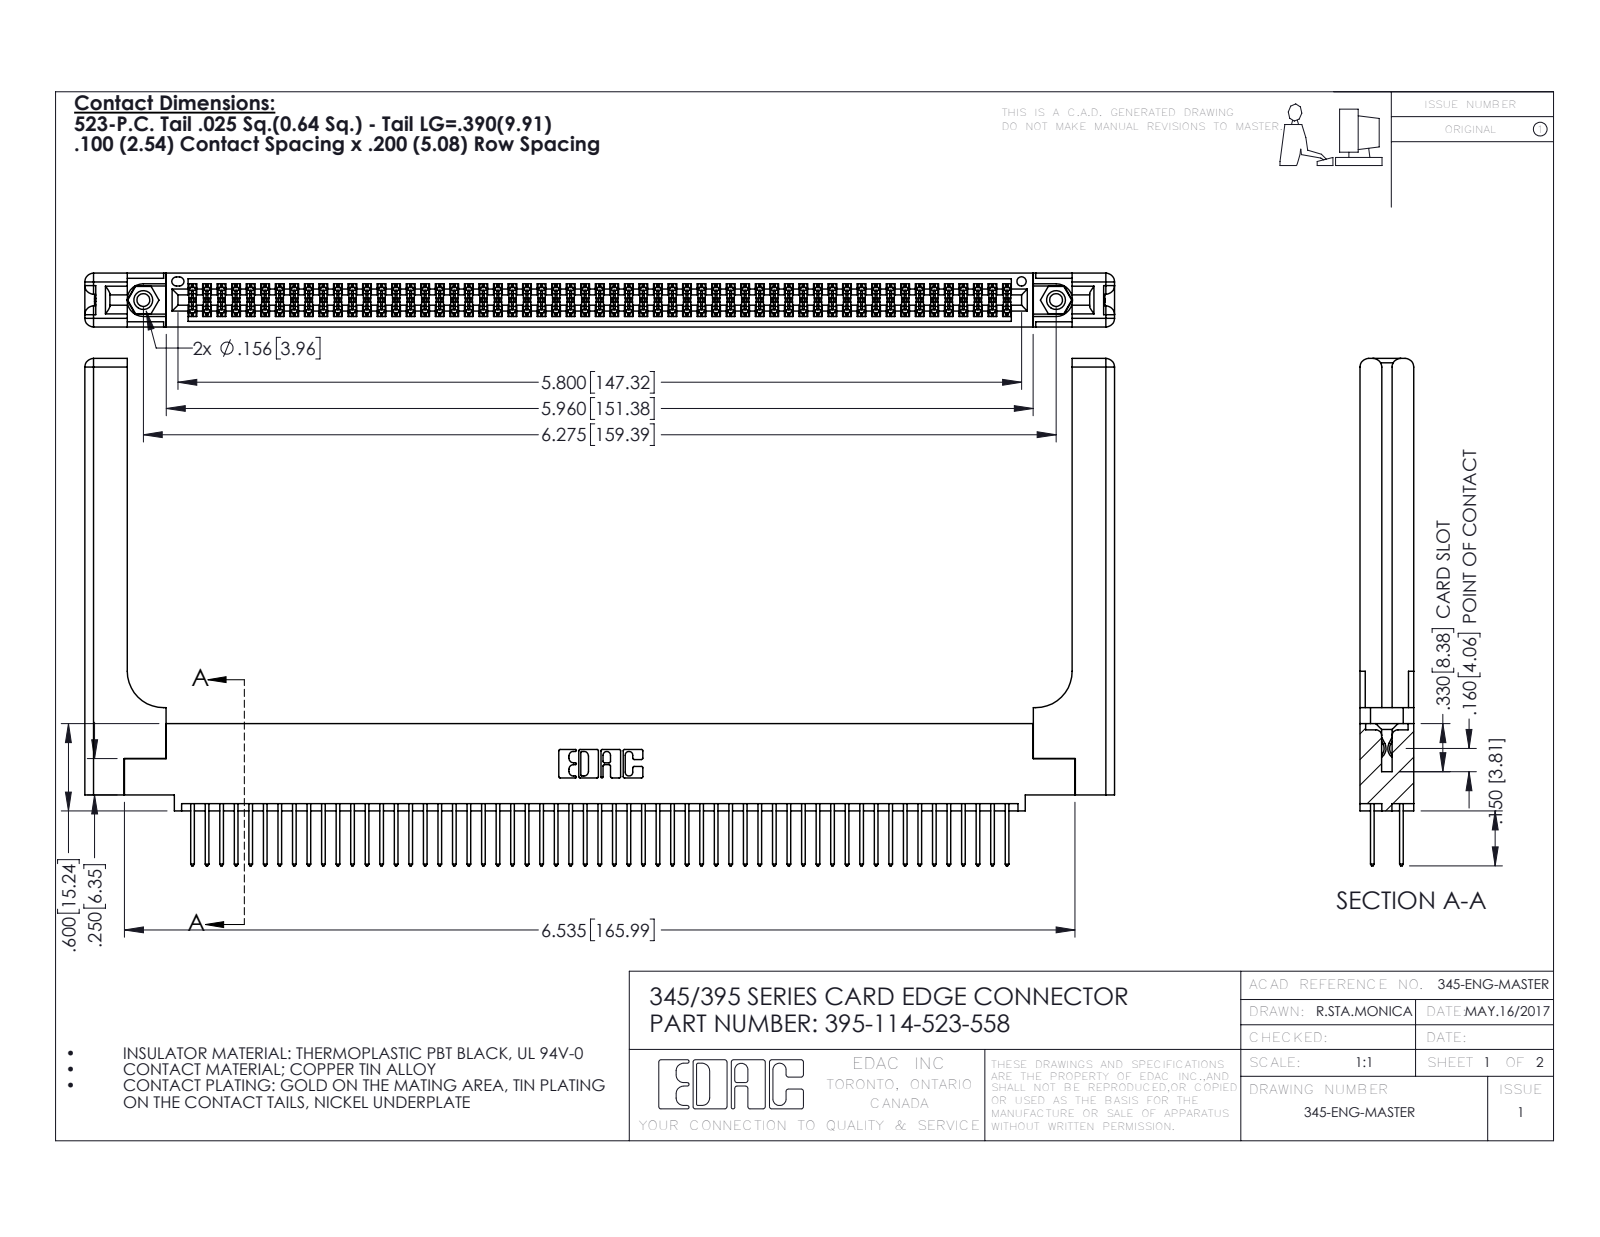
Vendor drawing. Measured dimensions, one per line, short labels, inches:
name: 345 Part_0.110 Offset - 0.156 Dia-TH; 345-250-001_345-250-001-102; 345-292-001_345-293-123; 395-114-523-558 (+1 more)
written by: SolidWorks 2016 (CONFIG_CONTROL_DESIGN)
unit: in
bodies: 119 solids, 6086 faces (3994 planar, 2032 cylindrical, 60 other)
size: 7.079 × 3.487 × 0.37
volume: 1.601 in³; area: 50.77 in²
holes: 2× ⌀0.089, 2× ⌀0.125, 2× ⌀0.156, 1× ⌀0.064
bosses: 2× ⌀0.155
rounds: 171× R0.006, 114× R0.01, 22× R0.01, 16× R0.06, 6× R0.007, 6× R0.031, 3× R0.026, 2× R0.014
face distances: 0.072, 0.298, 0.37, 0.098, 0.272, 0.025, 0.2, 0.225, 0.175, 0.148
hole spacings: 0.27, 6.039, 6.275
